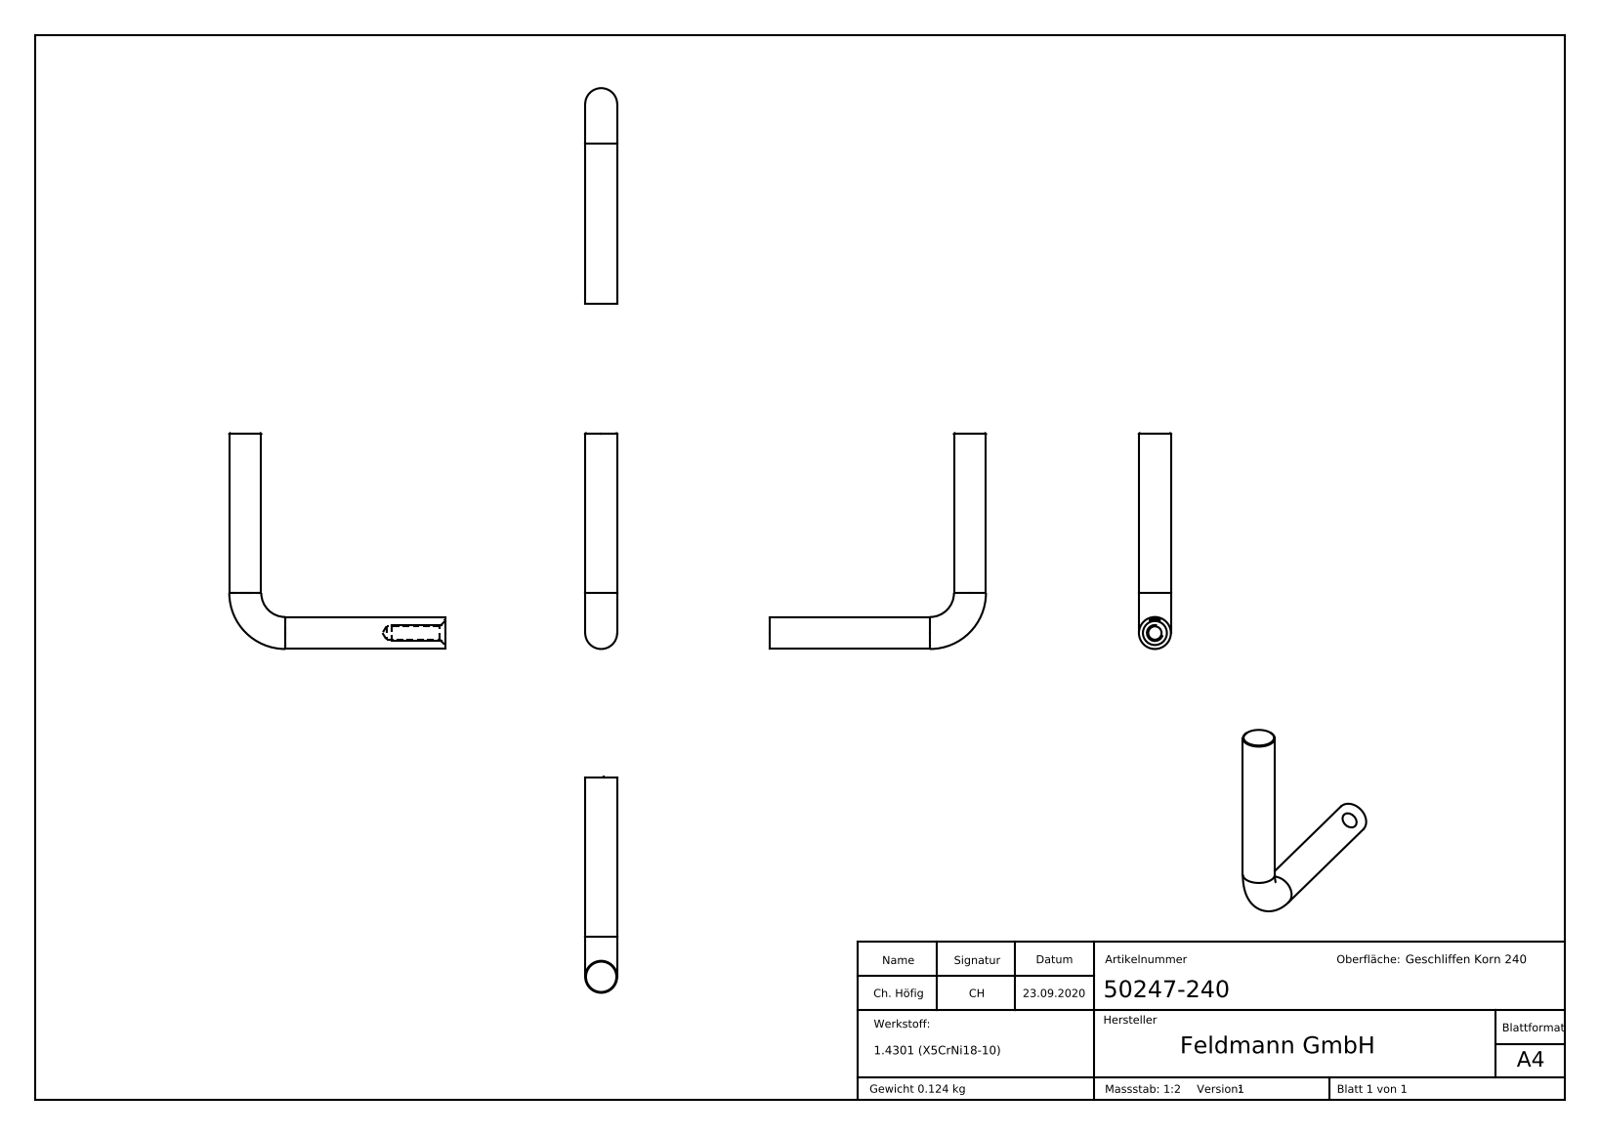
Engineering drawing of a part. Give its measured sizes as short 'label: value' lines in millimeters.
name: 50247-240
written by: SolidWorks 2018 (CONFIG_CONTROL_DESIGN)
unit: mm
bodies: 1 solid, 234 faces (134 planar, 6 cylindrical, 94 other)
size: 81 × 81 × 12
volume: 15 753 mm³; area: 5 969 mm²
holes: 1× ⌀5
bosses: 2× ⌀12
